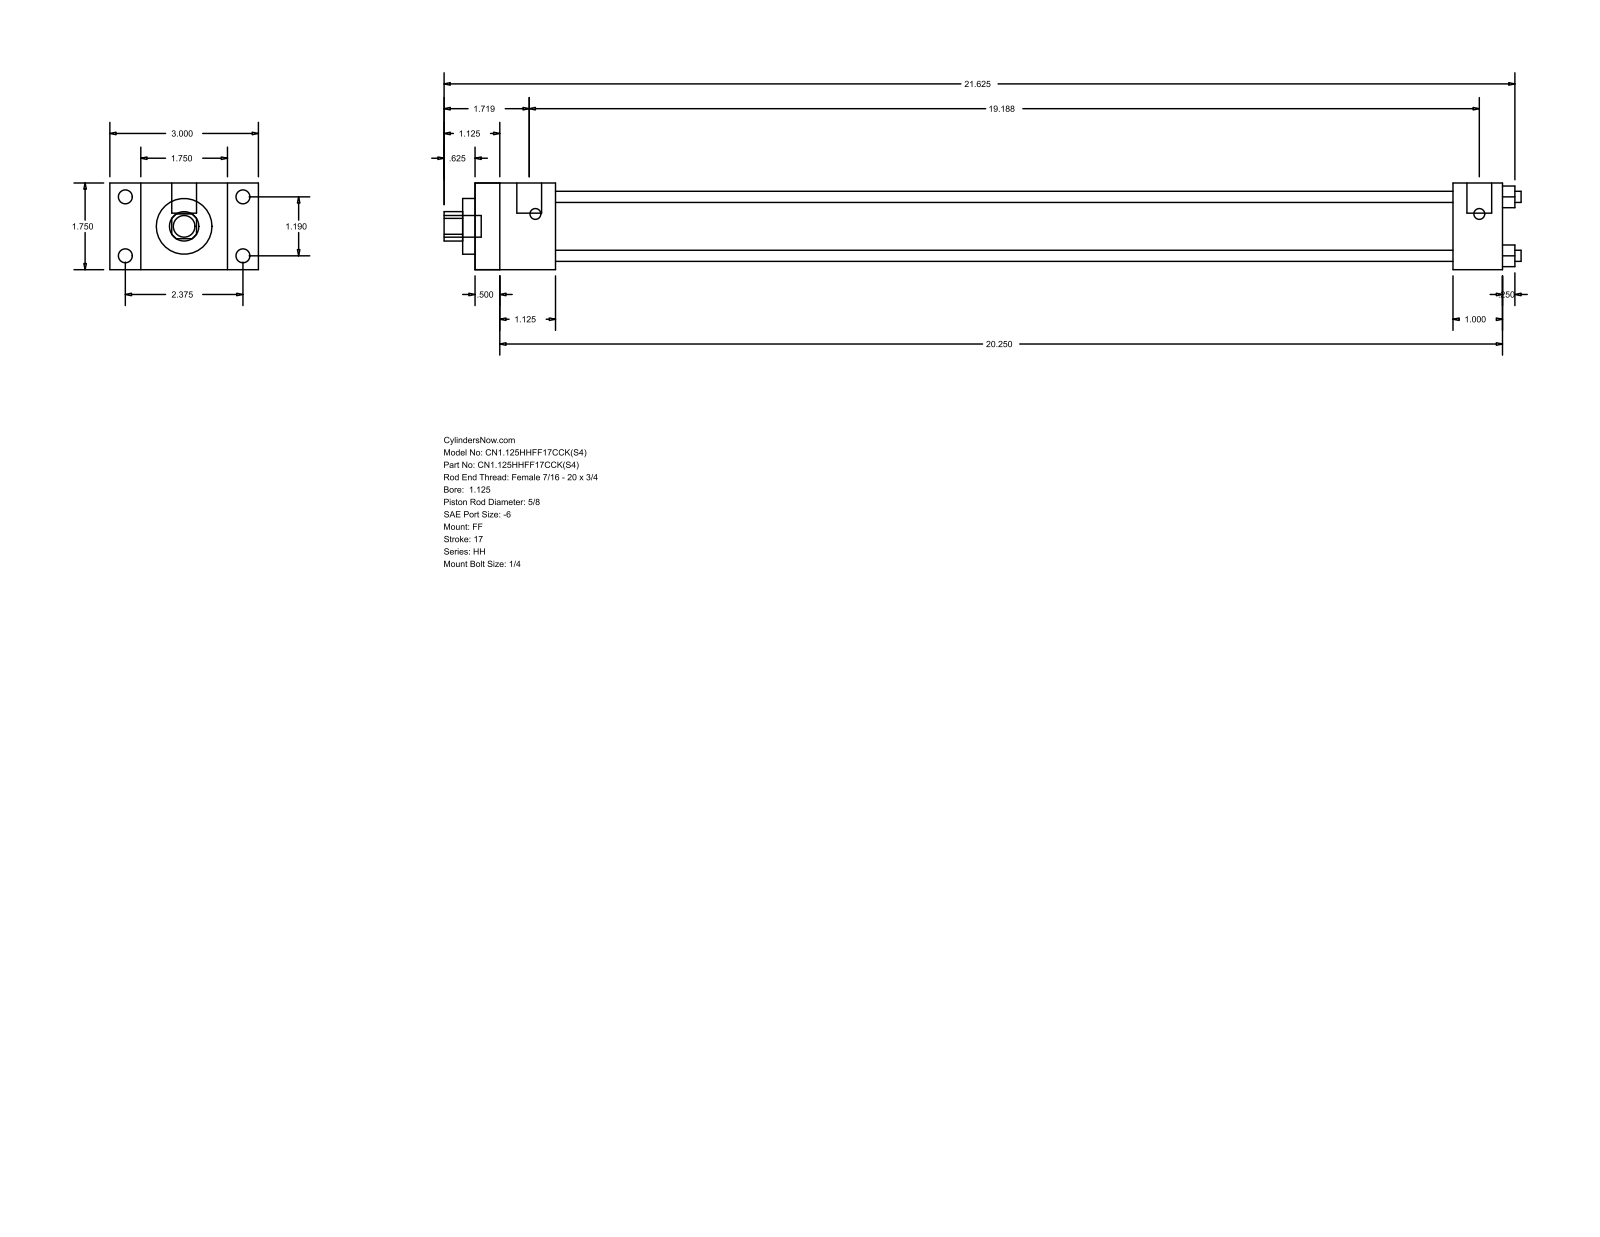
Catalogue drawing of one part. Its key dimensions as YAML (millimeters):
part_name: "HH_FF__0112_0.625"
step_written_by: "GSSL Pune (CONFIG_CONTROL_DESIGN)"
units: millimeters
bodies: {solids: 0, faces: 92, planar: 64, cylindrical: 28, other: 0}
overall_size: [552.45, 76.2, 44.45]
round_holes:
  - {diameter: 5.71, count: 4}
  - {diameter: 15.88, count: 1}
  - {diameter: 28.57, count: 1}
  - {diameter: 34.92, count: 1}
round_bosses_or_shafts:
  - {diameter: 7.14, count: 4}
  - {diameter: 5.56, count: 4}
  - {diameter: 12.7, count: 2}
  - {diameter: 11.11, count: 1}
partial_cylinders:
  - {radius: 7.54, count: 1}
face_to_face_distances: [44.46, 527.04, 12.69, 514.35, 15.87, 60.33, 28.58, 41.27, 501.64, 488.95]
hole_center_spacings: [21.37, 30.22, 42.74]
